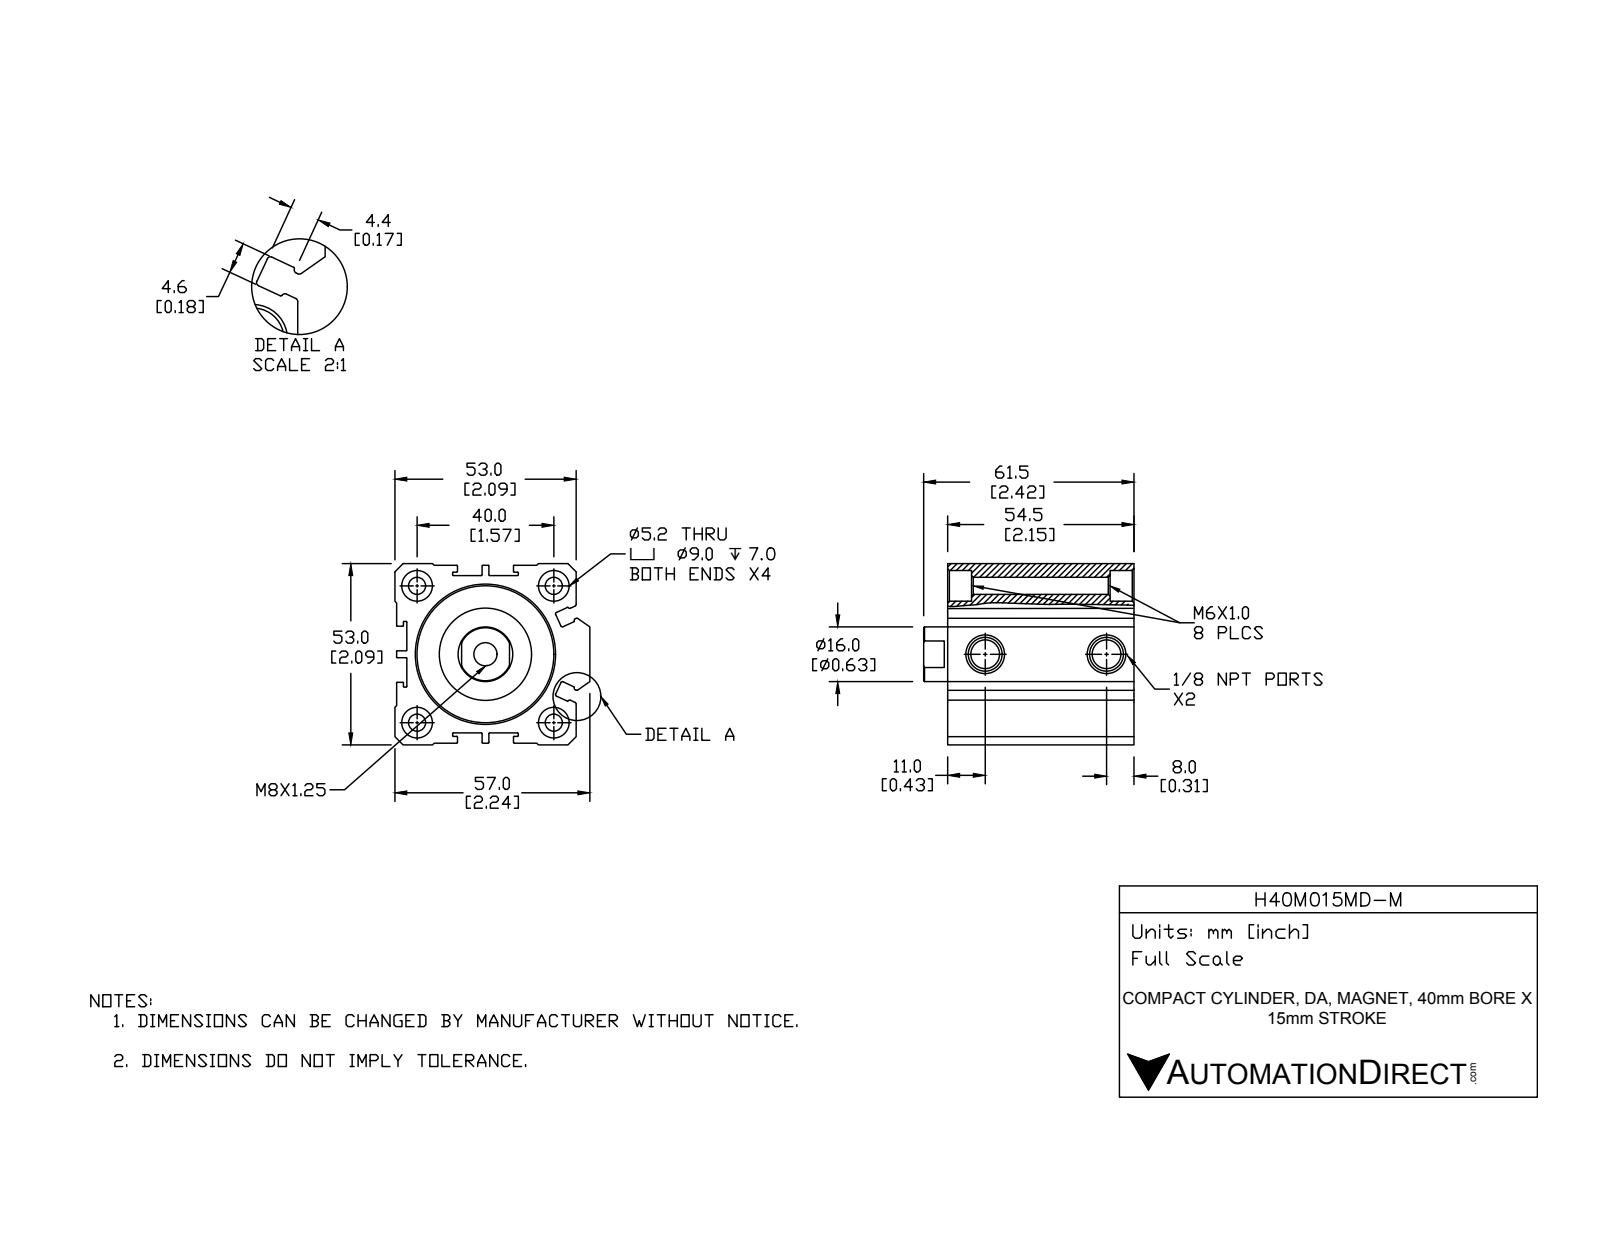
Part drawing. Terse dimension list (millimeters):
name: H40M015MD-M-BODY; H40M015MD-M; H40M015MD-M-PISTON
written by: SolidWorks 2015 (CONFIG_CONTROL_DESIGN)
unit: mm
bodies: 2 solids, 255 faces (99 planar, 103 cylindrical, 53 other)
size: 61.5 × 57 × 53
volume: 114 056 mm³; area: 40 852 mm²
holes: 4× ⌀5, 4× ⌀9, 2× ⌀8.43, 1× ⌀6.8, 1× ⌀16, 1× ⌀29.5, 1× ⌀40
bosses: 1× ⌀27, 1× ⌀25
rounds: 40× R0.2, 12× R0.5
face distances: 49.5, 3.5, 53, 0.5, 3, 52.5, 49, 54.5, 21.3, 37.95
hole spacings: 28.28, 40, 56.57, 35.5
